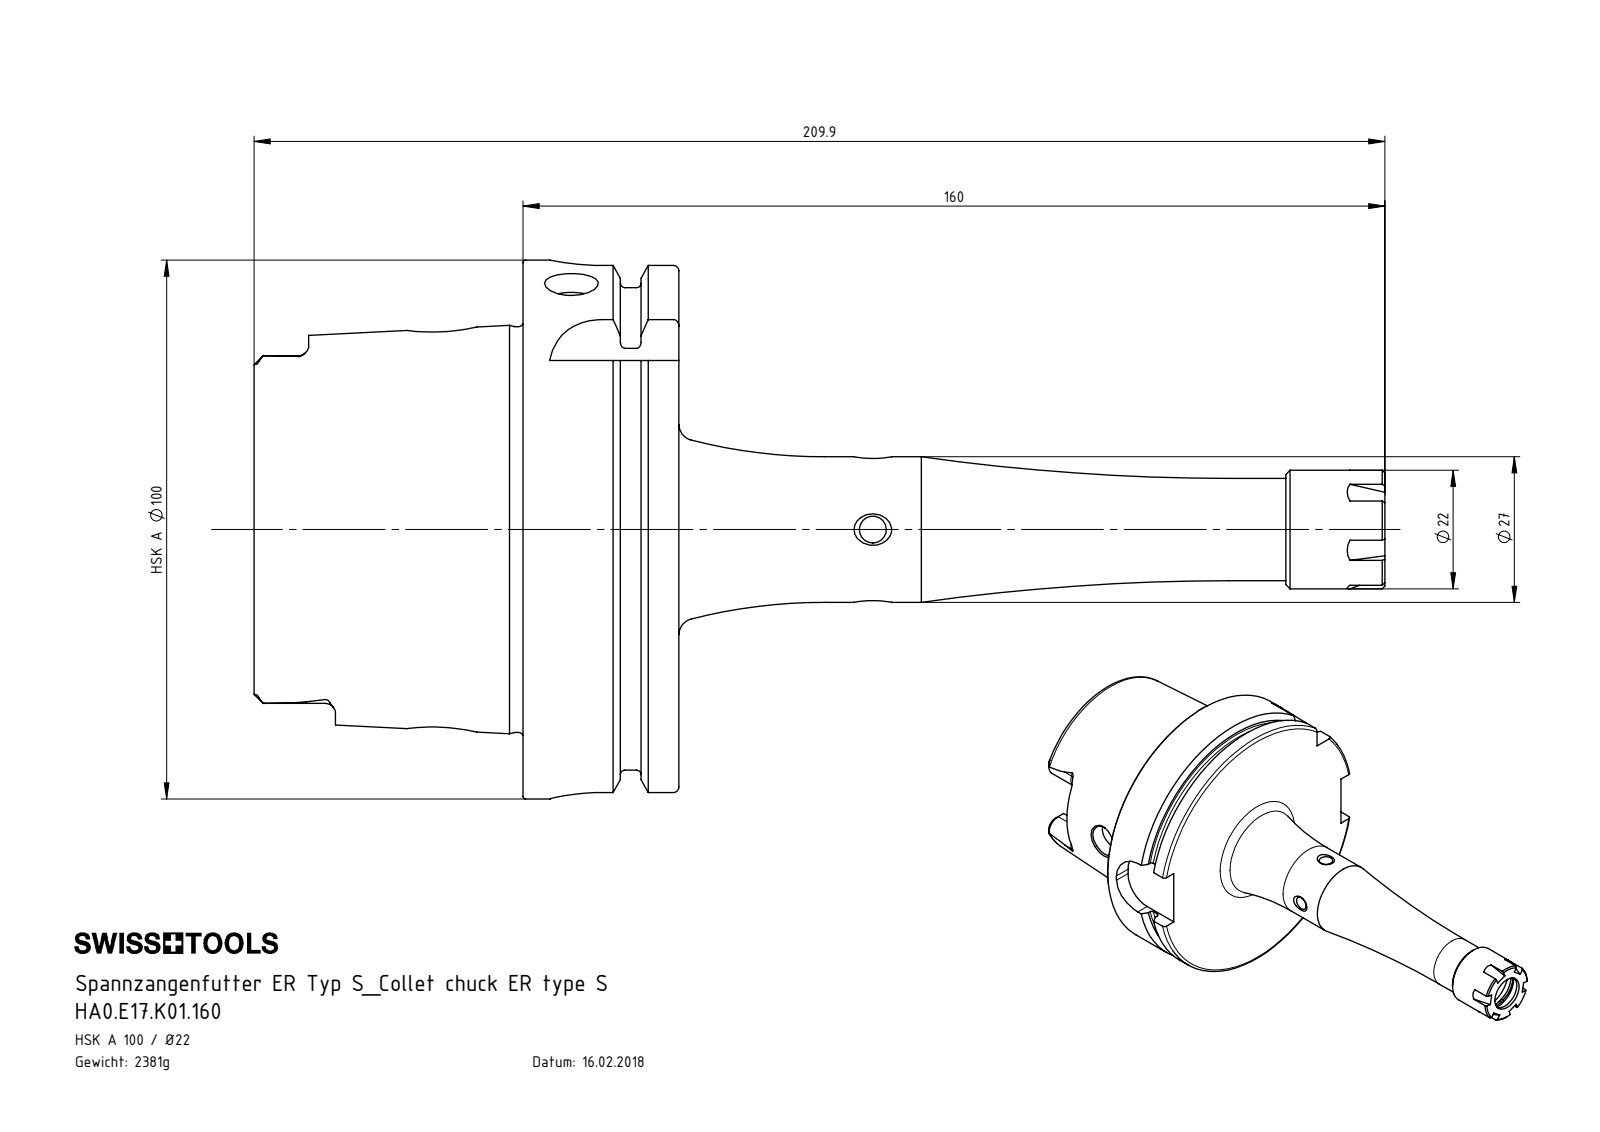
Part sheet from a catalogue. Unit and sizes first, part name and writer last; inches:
Units: inches
Overall size (bounding box): 8.264 × 3.937 × 3.937
Round holes (diameter × count): ⌀0.197 ×3, ⌀0.394 ×3, ⌀0.118 ×1, ⌀0.268 ×1, ⌀0.335 ×1, ⌀0.413 ×1, ⌀0.472 ×1, ⌀0.5 ×1, ⌀0.709 ×1, ⌀0.787 ×1, ⌀0.886 ×1, ⌀1.024 ×1
Round bosses / shafts (diameter × count): ⌀3.937 ×1, ⌀3.62 ×1, ⌀2.963 ×1, ⌀1.063 ×1, ⌀0.866 ×1, ⌀0.748 ×1, ⌀0.236 ×1
Partial cylindrical surfaces — rounded edges, fillets, slot ends (radius × count): R0.075 ×6, R0.192 ×4, R0.394 ×4, R0.303 ×2
Main face-to-face distances: 1.14, 0.49, 0.65, 1.965, 2.455, 3.104, 3.079, 1.114, 0.624, 0.026
Hole centre spacings: 2.281, 3.148
Volume: 18.51 in³ · Surface area: 100.3 in²
Bodies: 3 solids, 301 faces (99 planar, 83 cylindrical, 119 other)
Part name (STEP PRODUCT): E17-ER1.001.018; ERU-AN2.K01.016_A; HA0.E17.K01.160; HA0-E17.K01.160_C_Fertigbearbeitung
STEP written by: SolidWorks 2017 (CONFIG_CONTROL_DESIGN)
